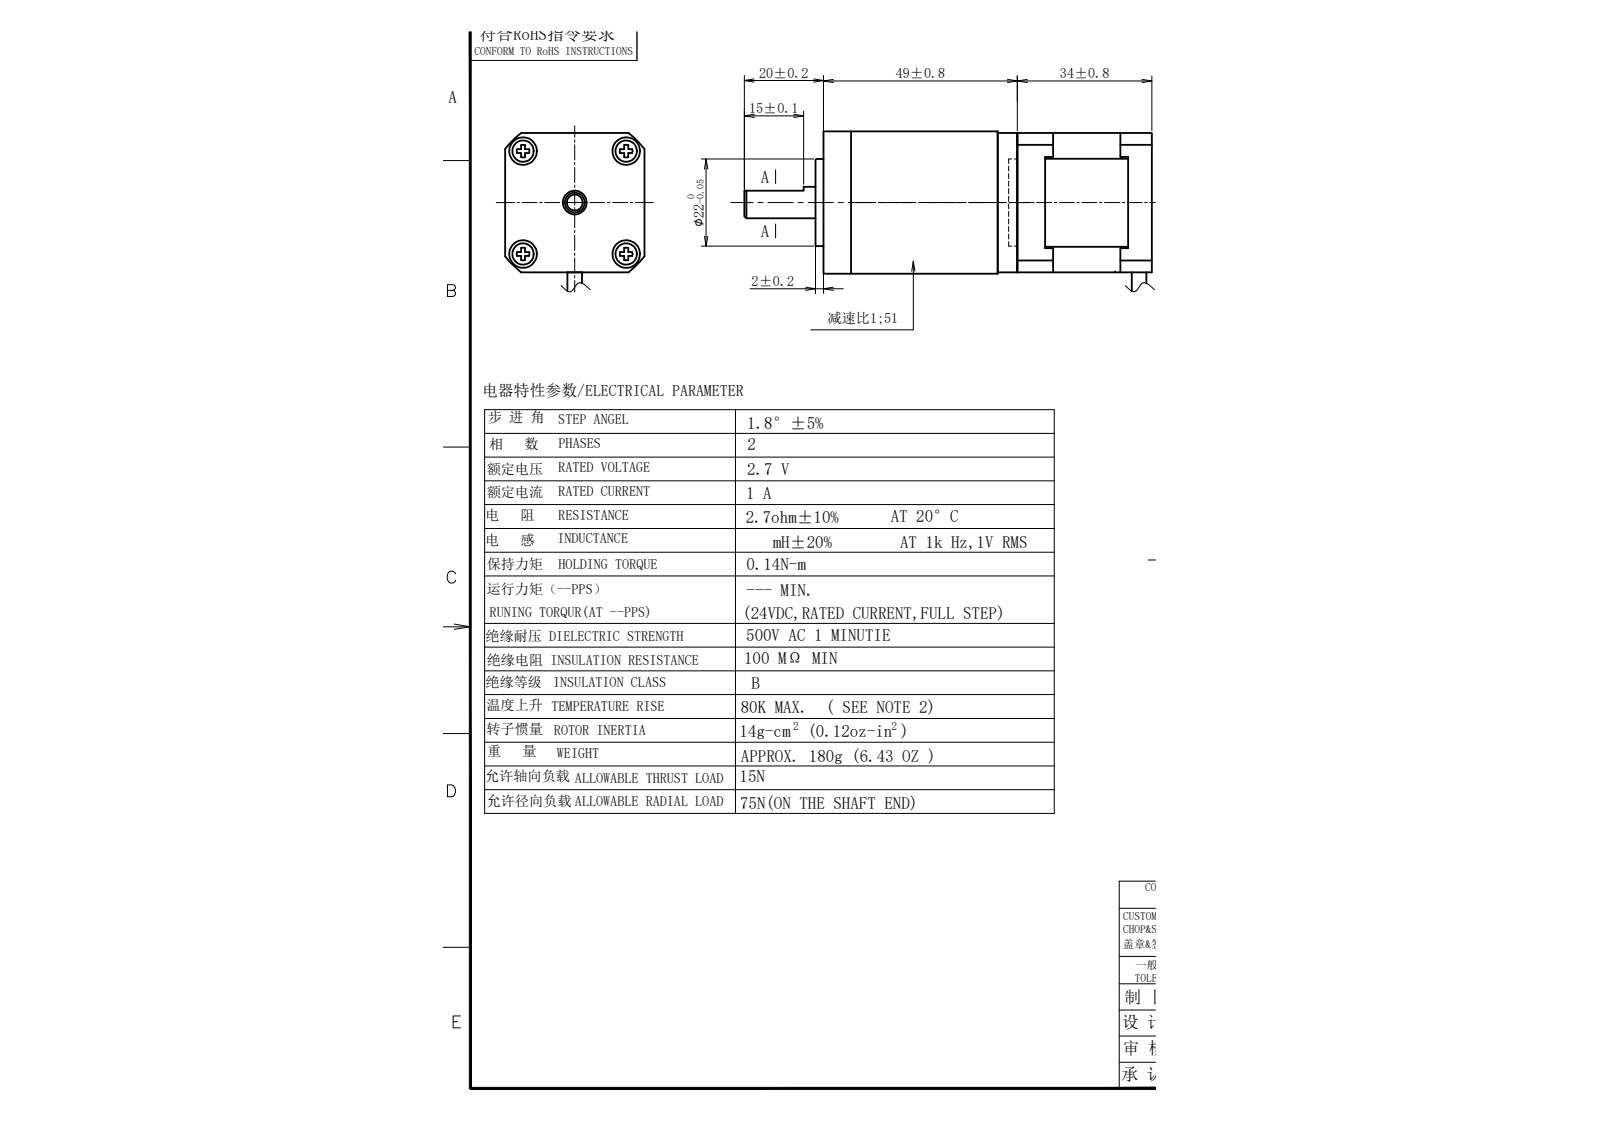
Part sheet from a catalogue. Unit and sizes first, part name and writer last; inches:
Units: inches
Overall size (bounding box): 4.055 × 2.506 × 1.417
Round holes (diameter × count): ⌀0.098 ×8, ⌀0.081 ×4, ⌀0.114 ×4, ⌀0.13 ×4, ⌀0.134 ×4, ⌀0.197 ×4, ⌀0.228 ×4, ⌀0.118 ×3, ⌀0.047 ×2, ⌀0.291 ×1, ⌀0.315 ×1, ⌀0.492 ×1
Round bosses / shafts (diameter × count): ⌀0.197 ×5, ⌀0.118 ×4, ⌀0.047 ×4, ⌀1.417 ×1, ⌀0.866 ×1, ⌀0.862 ×1, ⌀0.846 ×1, ⌀0.433 ×1
Partial cylindrical surfaces — rounded edges, fillets, slot ends (radius × count): R0.008 ×92, R0.11 ×92, R0.016 ×8, R0.017 ×8, R0.012 ×6, R0.118 ×2, R0.827 ×2, R0.187 ×1
Main face-to-face distances: 1.378, 0.197, 0.827, 0.276, 0.236, 1.299, 0.472, 1.102, 1.85, 1.535
Hole centre spacings: 0.422, 0.513, 0.551, 0.78, 0.91, 1.019, 1.18, 0.172
Volume: 4.843 in³ · Surface area: 59.06 in²
Bodies: 20 solids, 816 faces (154 planar, 541 cylindrical, 121 other)
Part name (STEP PRODUCT): PLA36-002输出轴; 35D16-A前端盖; 定子; 35D16-B后端盖 (+8 more)
STEP written by: SolidWorks 2020 (CONFIG_CONTROL_DESIGN)
